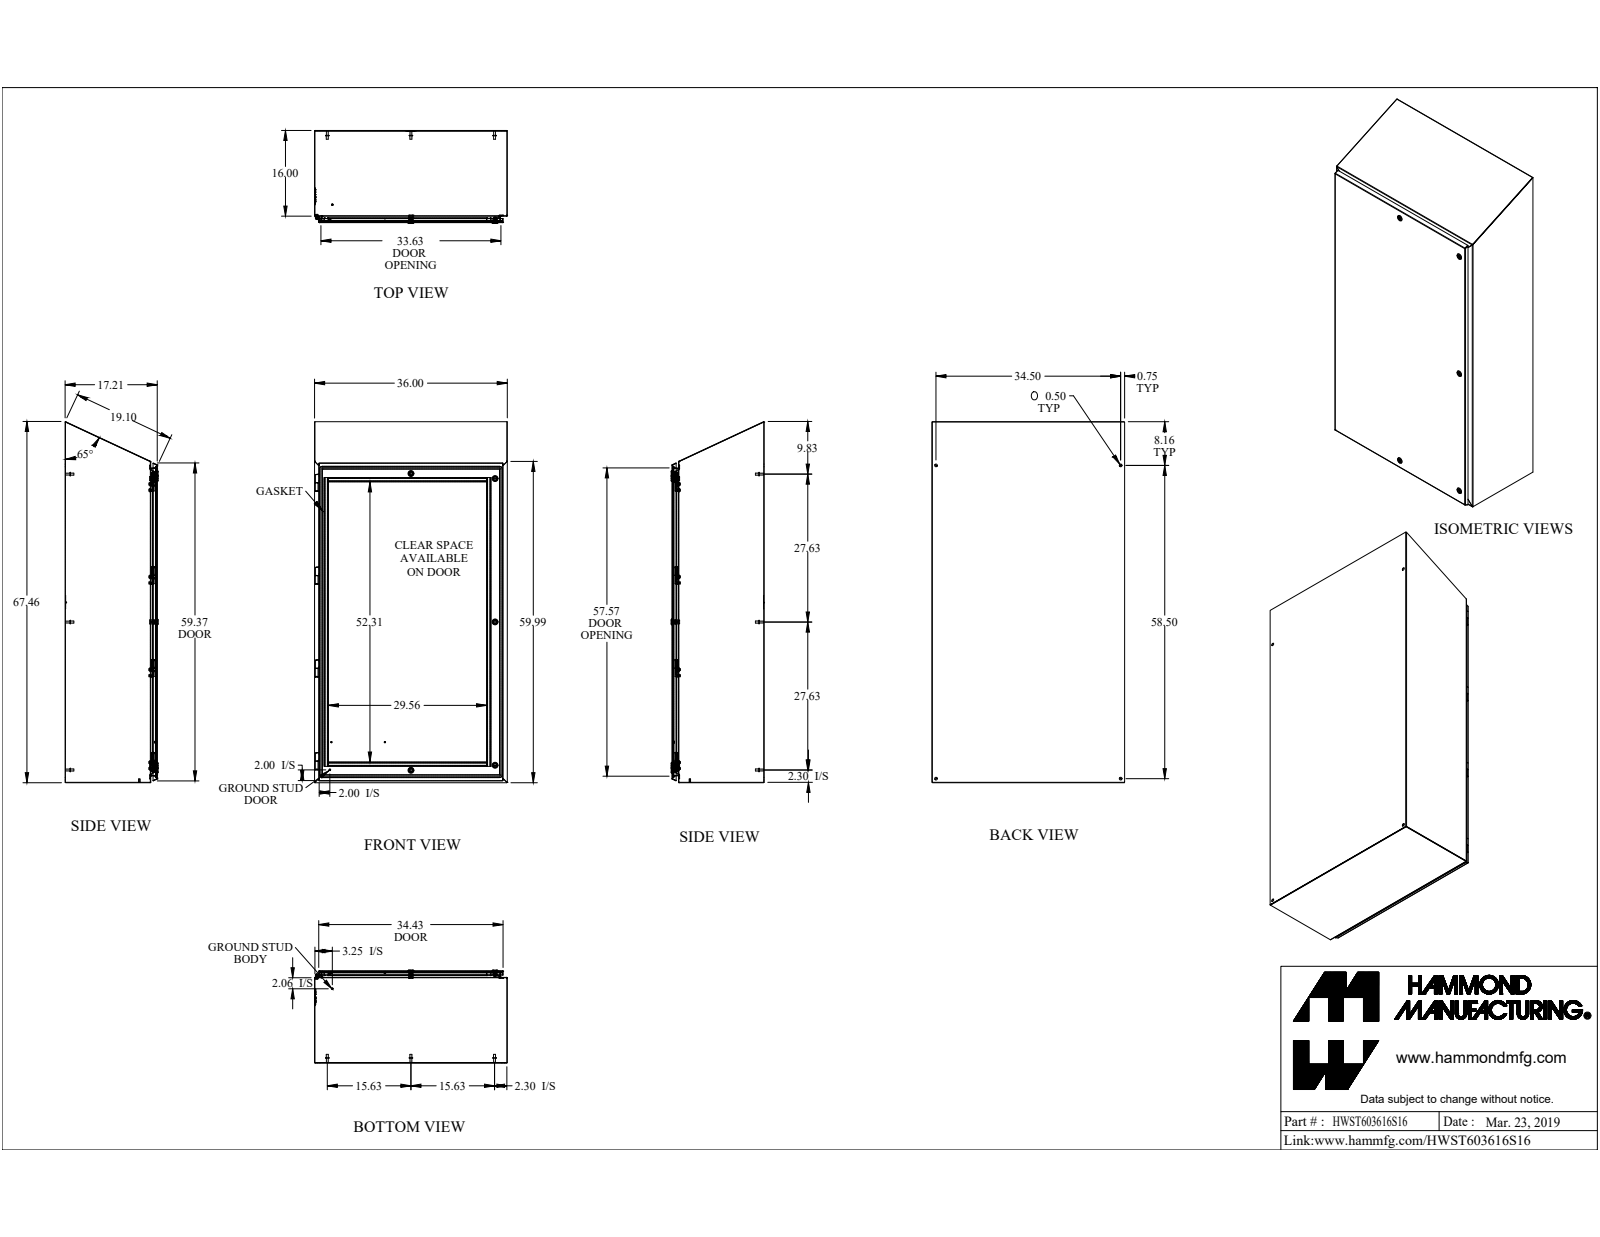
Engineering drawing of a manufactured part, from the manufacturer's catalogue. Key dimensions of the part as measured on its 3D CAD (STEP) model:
Part name (STEP PRODUCT): HWST603616S16
STEP written by: SolidWorks 2019 (AUTOMOTIVE_DESIGN)
Units: inches
Bodies: 86 solids, 1971 faces (1216 planar, 539 cylindrical, 216 other)
Overall size (bounding box): 67.409 × 36 × 17.37
Volume: 645.8 in³ · Surface area: 18 173 in²
Round holes (diameter × count): ⌀0.194 ×16, ⌀0.24 ×16, ⌀0.5 ×9, ⌀0.275 ×8, ⌀0.197 ×5, ⌀0.387 ×5, ⌀0.63 ×5, ⌀0.768 ×5, ⌀0.13 ×2, ⌀0.24 ×1, ⌀3.5 ×1
Round bosses / shafts (diameter × count): ⌀0.226 ×16, ⌀0.625 ×11, ⌀0.65 ×8, ⌀0.375 ×8, ⌀0.332 ×8, ⌀0.236 ×6, ⌀1.1 ×5, ⌀0.25 ×4
Partial cylindrical surfaces — rounded edges, fillets, slot ends (radius × count): R0.039 ×32, R0.125 ×26, R0.043 ×24, R0.25 ×24, R0.012 ×20, R0.036 ×17, R0.108 ×17, R0.03 ×16
Main face-to-face distances: 0.072, 0.072, 17.138, 17.066, 17.138, 17.21, 35.856, 35.928, 35.928, 36
Hole centre spacings: 17.324, 1.142, 17.325, 34.649, 1.142, 16.183, 34.649, 17.326
